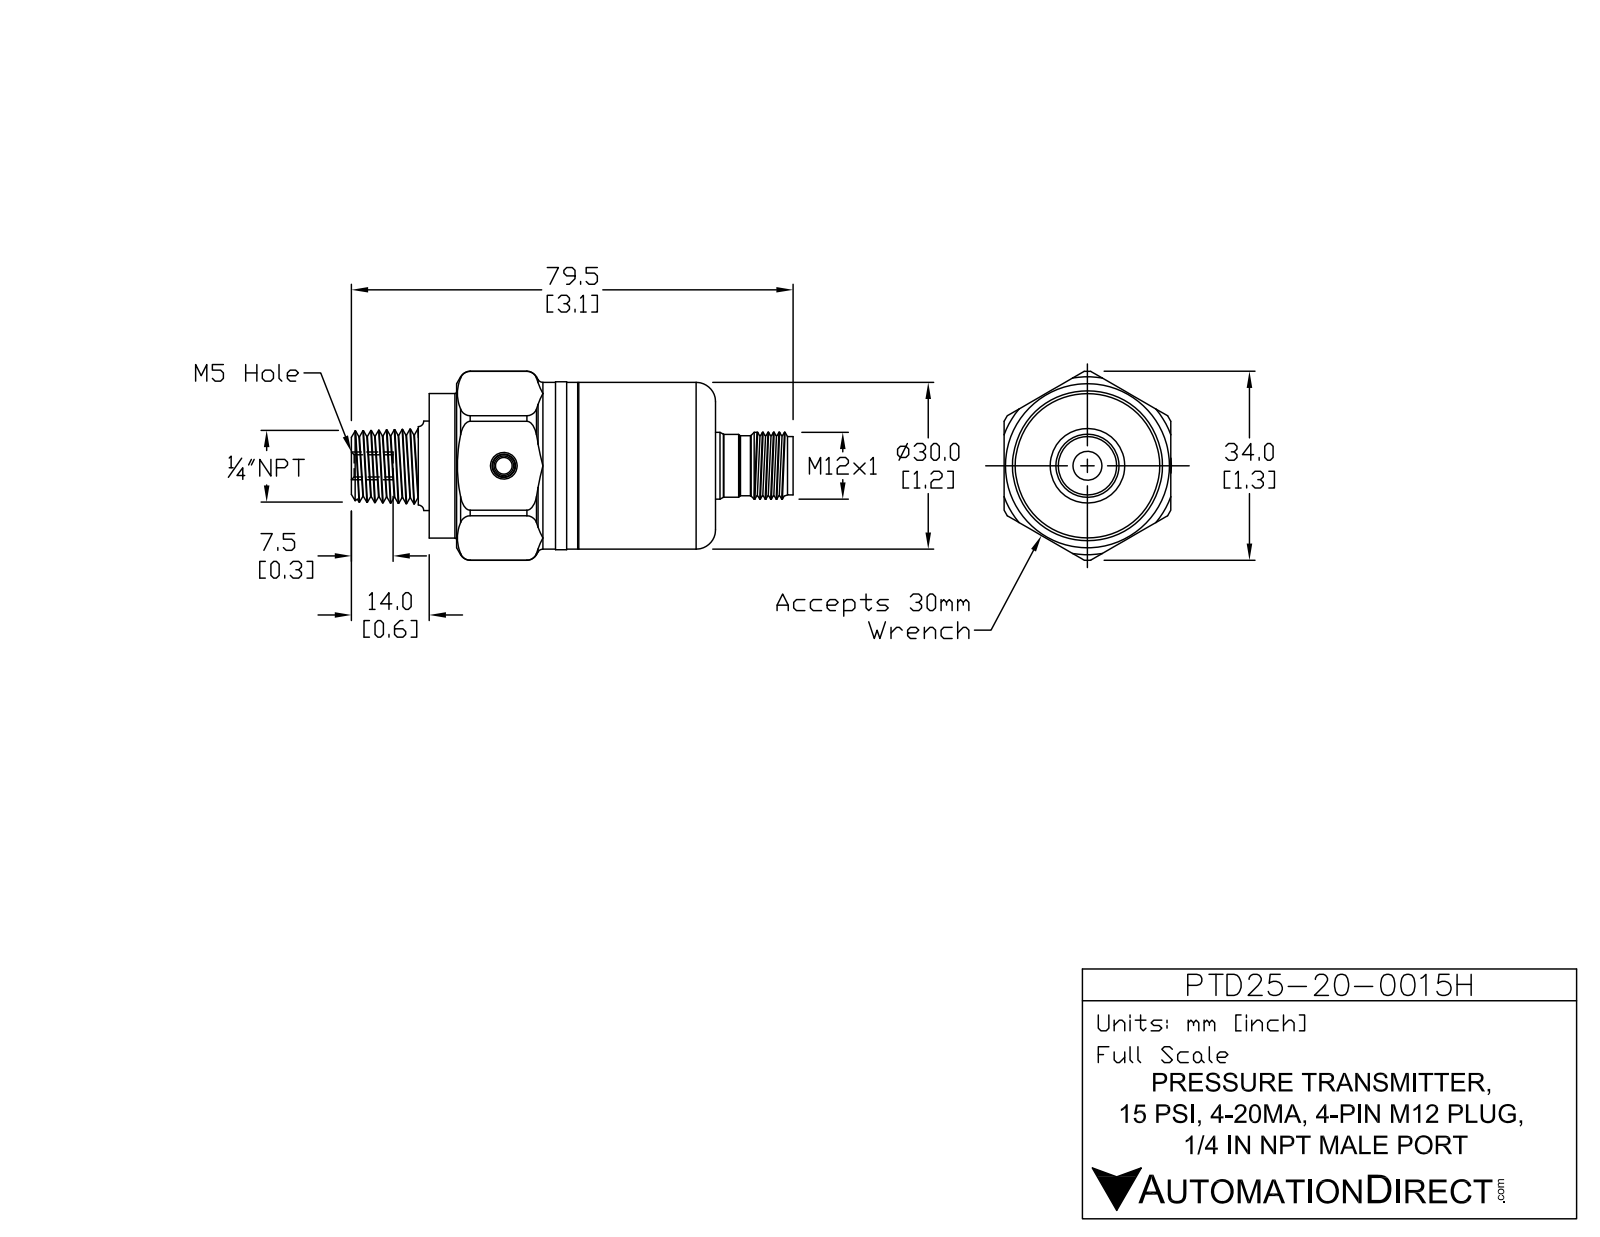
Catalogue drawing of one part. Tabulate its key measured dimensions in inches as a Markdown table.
| quantity | value |
| --- | --- |
| part name | PTD25-20-0015H |
| STEP written by | SolidWorks 2017 (AUTOMOTIVE_DESIGN) |
| units | inches |
| bodies | 1 solid, 124 faces (36 planar, 59 cylindrical, 29 other) |
| overall size | 3.13 × 1.33 × 1.248 |
| volume | 2.393 in³ |
| surface area | 12.54 in² |
| round holes (diameter × count) | 0.157 × 1, 0.335 × 1 |
| round bosses / shafts (diameter × count) | 1.183 × 1, 1.181 × 1, 1.022 × 1, 0.551 × 1, 0.531 × 1, 0.472 × 1 |
| partial cylindrical surfaces (radius × count) | 0.148 × 1, 0.667 × 1 |
| main face-to-face distances | 2.008, 1.18, 1.181, 1.89, 0.118, 2.559, 0.669, 0.551, 1.181, 0.222 |
